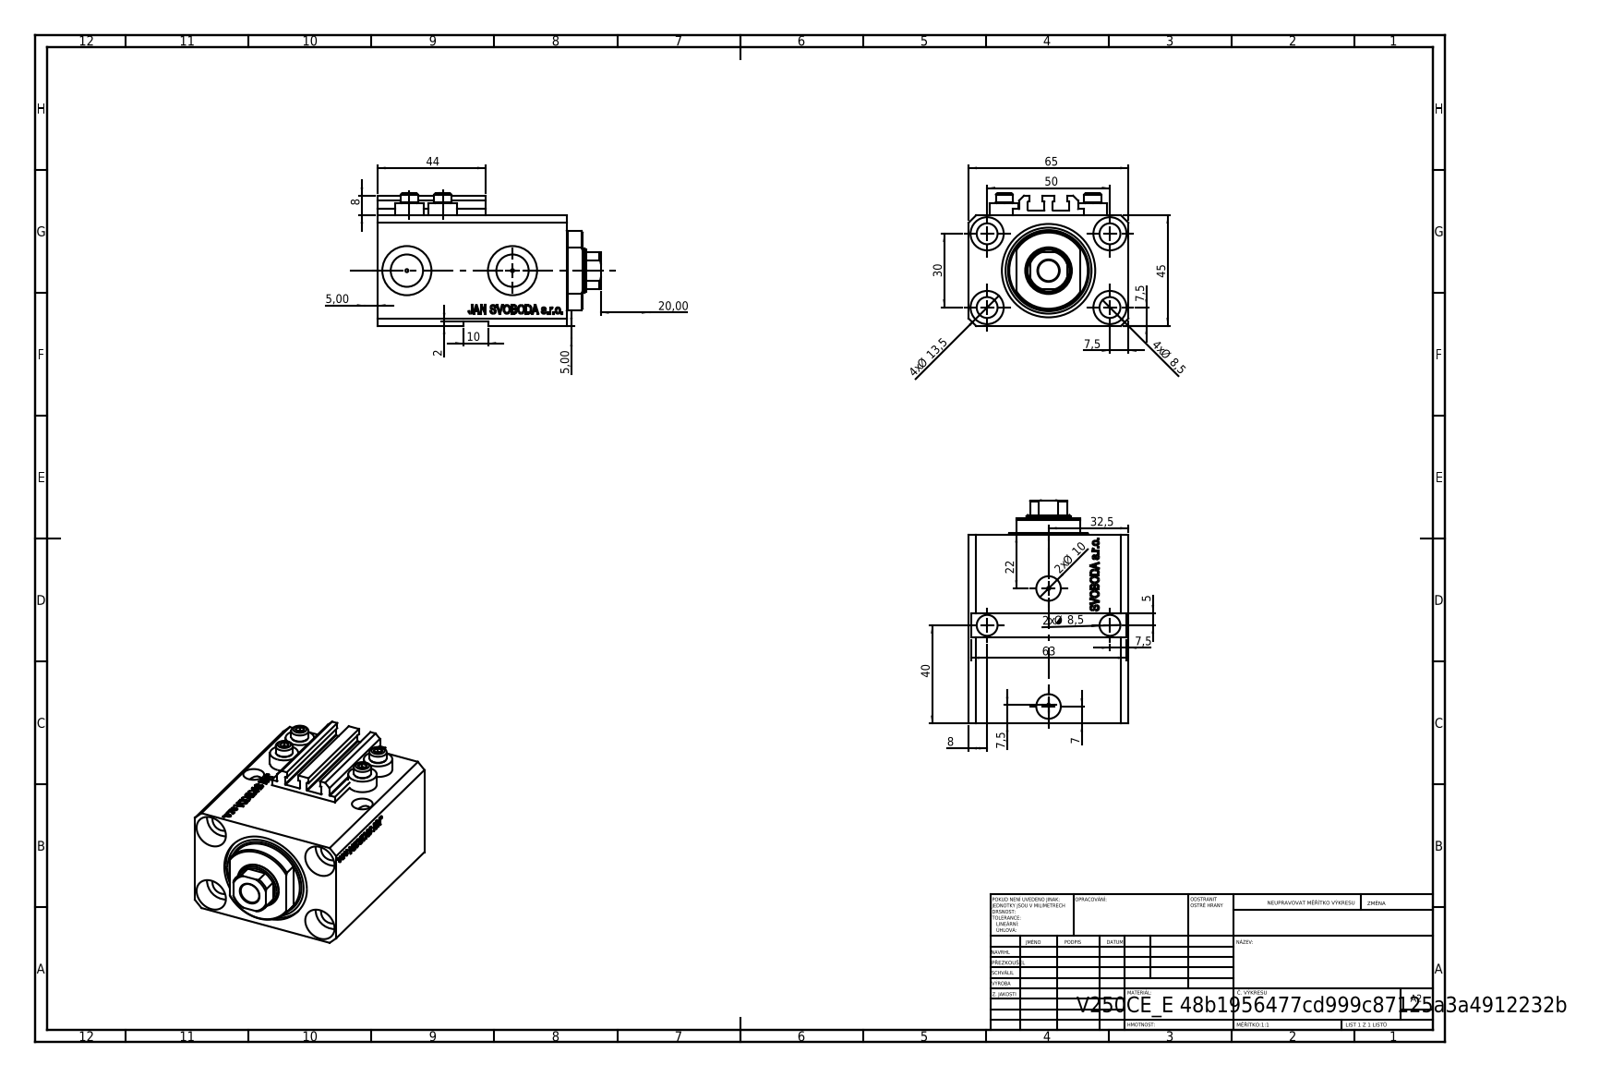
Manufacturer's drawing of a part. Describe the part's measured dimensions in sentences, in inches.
The part is named "V250CE_VC_E; V250CE_C_VCP; V250CE_E_Body; ALLEN BOLT V250CE". Its 3-D file was written by "SolidWorks 2019 (CONFIG_CONTROL_DESIGN)". It is 8 solids with 1067 faces: 511 planar, 126 cylindrical and 430 other. Overall it measures 3.579 by 2.559 by 2.126 inches. Its volume is 12.19 cubic inches and its surface area 95 square inches. Round holes: 7 of diameter 0.335, 4 of diameter 0.049, 4 of diameter 0.157, 4 of diameter 0.531, 2 of diameter 0.394, 2 of diameter 0.518, 2 of diameter 0.787, 1 of diameter 0.709, 1 of diameter 0.984, 1 of diameter 1.496. Round bosses or shafts: 4 of diameter 0.457, 4 of diameter 0.276. Partial cylindrical surfaces (rounded edges, fillets, slot ends): 10 of radius 0.008, 1 of radius 0.335, 1 of radius 0.63. The main face-to-face distances are 1.772, 2.559, 2.043, 3.031, 0.988, 0.079, 0.272, 2.76, 0.118, 0.354. The hole center spacings are 1.148, 1.969, 0.535, 0.595, 0.741, 0.747, 1.032, 1.048.
